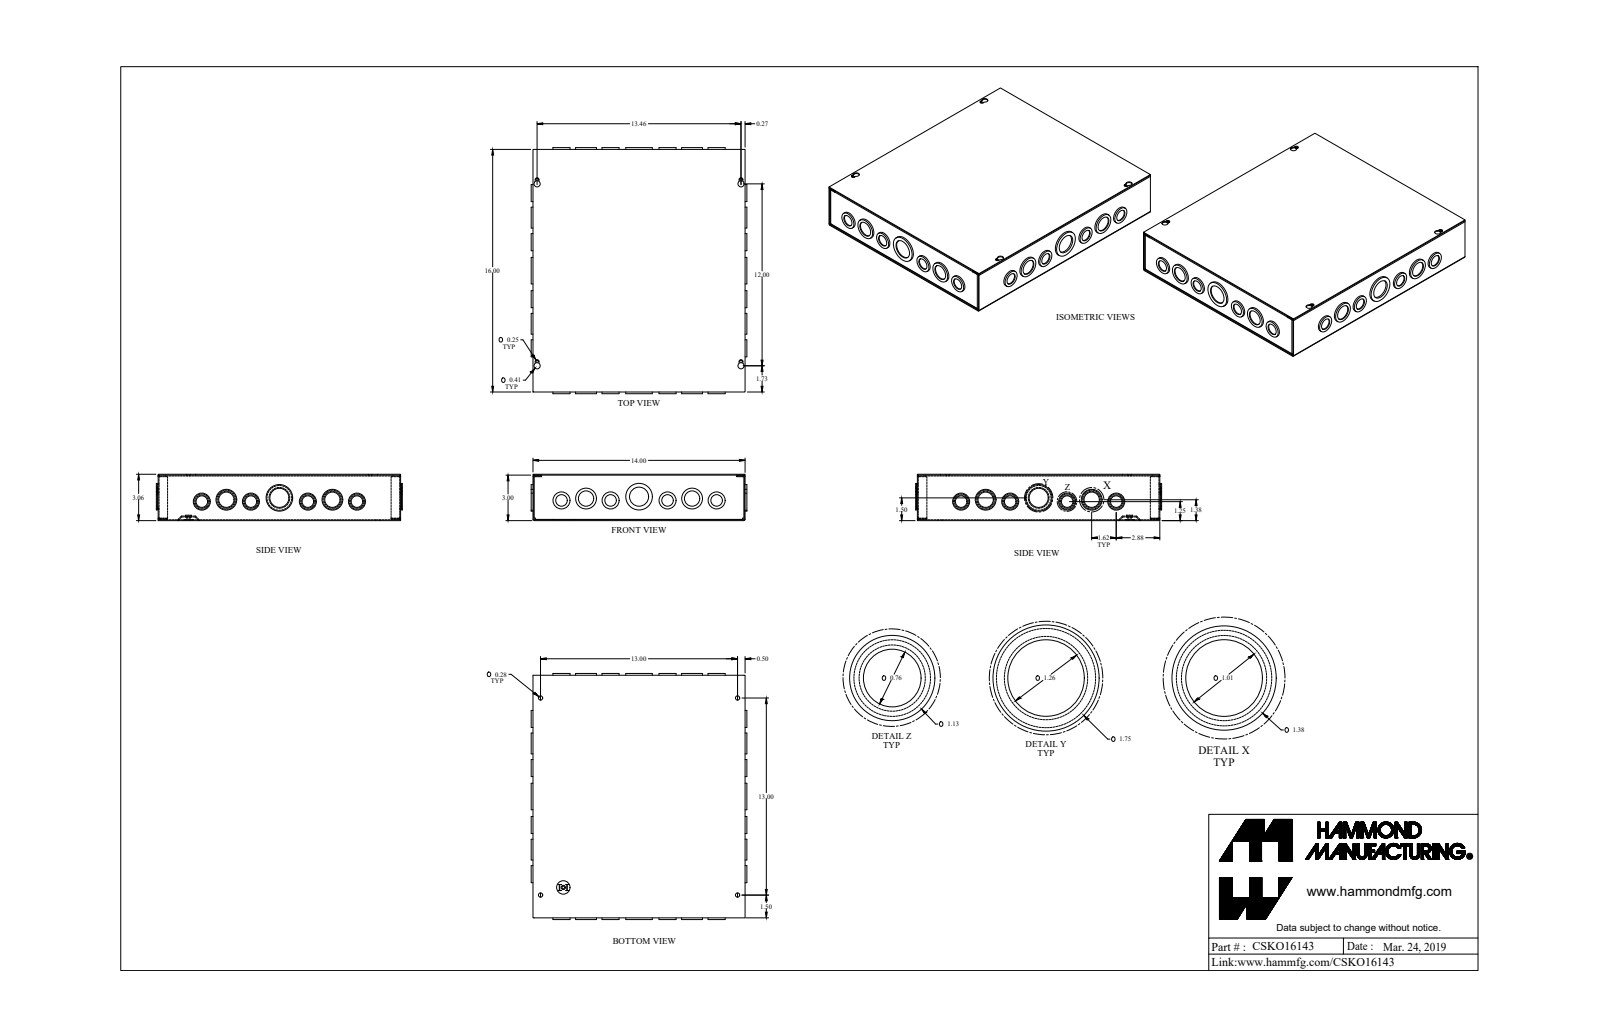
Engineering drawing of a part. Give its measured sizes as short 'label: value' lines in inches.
name: CSKO16143_Default
written by: SolidWorks 2019 (CONFIG_CONTROL_DESIGN)
unit: in
bodies: 4 solids, 541 faces (237 planar, 296 cylindrical, 8 other)
size: 16.234 × 14.234 × 3.057
volume: 39.03 in³; area: 1 382 in²
holes: 12× ⌀1.011, 8× ⌀0.761, 6× ⌀1.261, 5× ⌀0.17, 4× ⌀0.281, 2× ⌀1.636, 1× ⌀0.5
bosses: 10× ⌀1.125, 8× ⌀0.875, 5× ⌀1.375, 4× ⌀1.125, 4× ⌀0.875, 3× ⌀1.375, 2× ⌀1.75, 1× ⌀0.492
rounds: 12× R0.029, 12× R0.086, 8× R0.057, 4× R0.125, 4× R0.203
face distances: 0.057, 3, 2.943, 3.057, 13.943, 15.943, 14, 16, 0.114, 13.886
hole spacings: 1.625, 7, 0.55, 1.896, 3.24, 3.502, 5.126, 5.381
